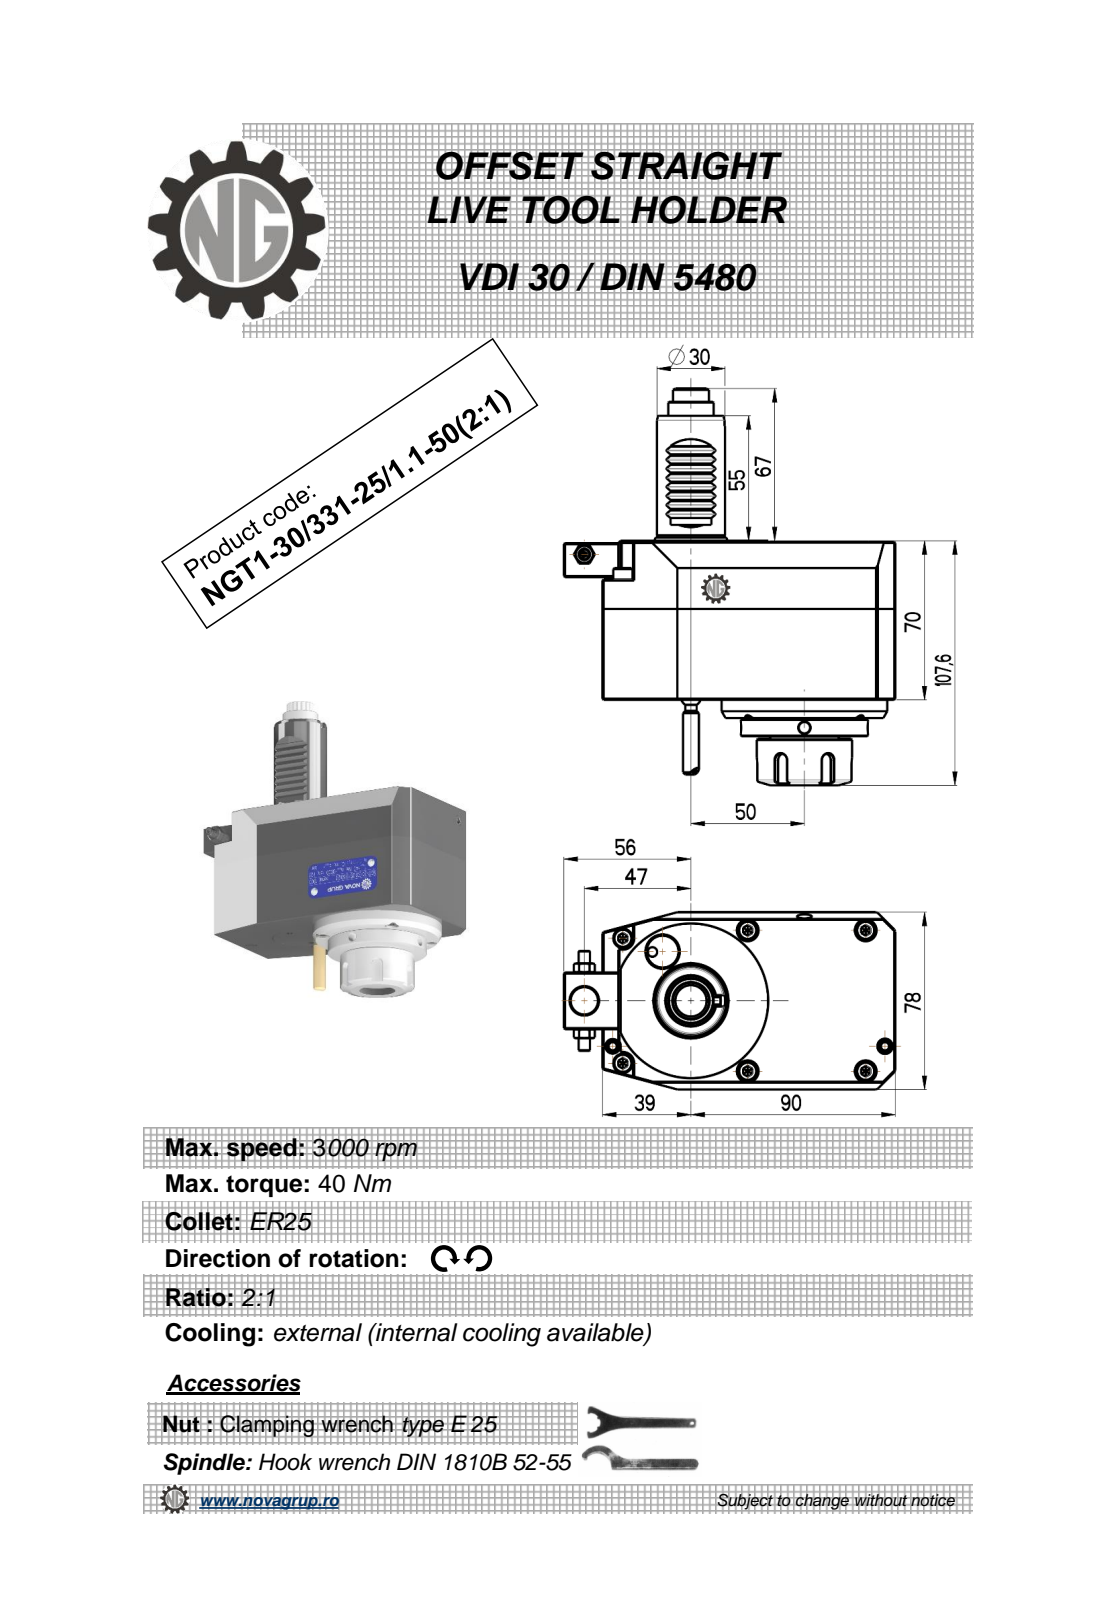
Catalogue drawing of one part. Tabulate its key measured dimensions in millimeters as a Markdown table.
| quantity | value |
| --- | --- |
| part name | NGT1_30_331_25_1_1_50_2_1 |
| STEP written by | PRO/ENGINEER BY PARAMETRIC TECHNOLOGY CORPORATION, 2010280 (CONFIG_CONTROL_DESIGN) |
| units | millimeters |
| bodies | 1 solid, 483 faces (168 planar, 167 cylindrical, 148 other) |
| overall size | 174.6 × 146 × 78 |
| volume | 793 063 mm³ |
| surface area | 67 874 mm² |
| round holes (diameter × count) | 5 × 2, 2.5 × 1, 3 × 1, 4.2 × 1, 9.5 × 1, 12 × 1, 14 × 1, 22 × 1, 26.4 × 1 |
| round bosses / shafts (diameter × count) | 8 × 2, 5 × 2, 73 × 1, 56 × 1, 42 × 1, 33 × 1, 30 × 1, 20 × 1 |
| partial cylindrical surfaces (radius × count) | 1.98 × 36, 0.16 × 12, 0.26 × 12, 0.3 × 8, 3 × 5, 4.5 × 2, 7.08 × 1, 7.92 × 1 |
| main face-to-face distances | 78, 70, 8, 130, 16, 86, 69, 0.5, 1, 7.5 |
| hole center spacings | 12.5, 21.5, 25, 40.73, 47, 51.68, 73.75, 123.38 |
